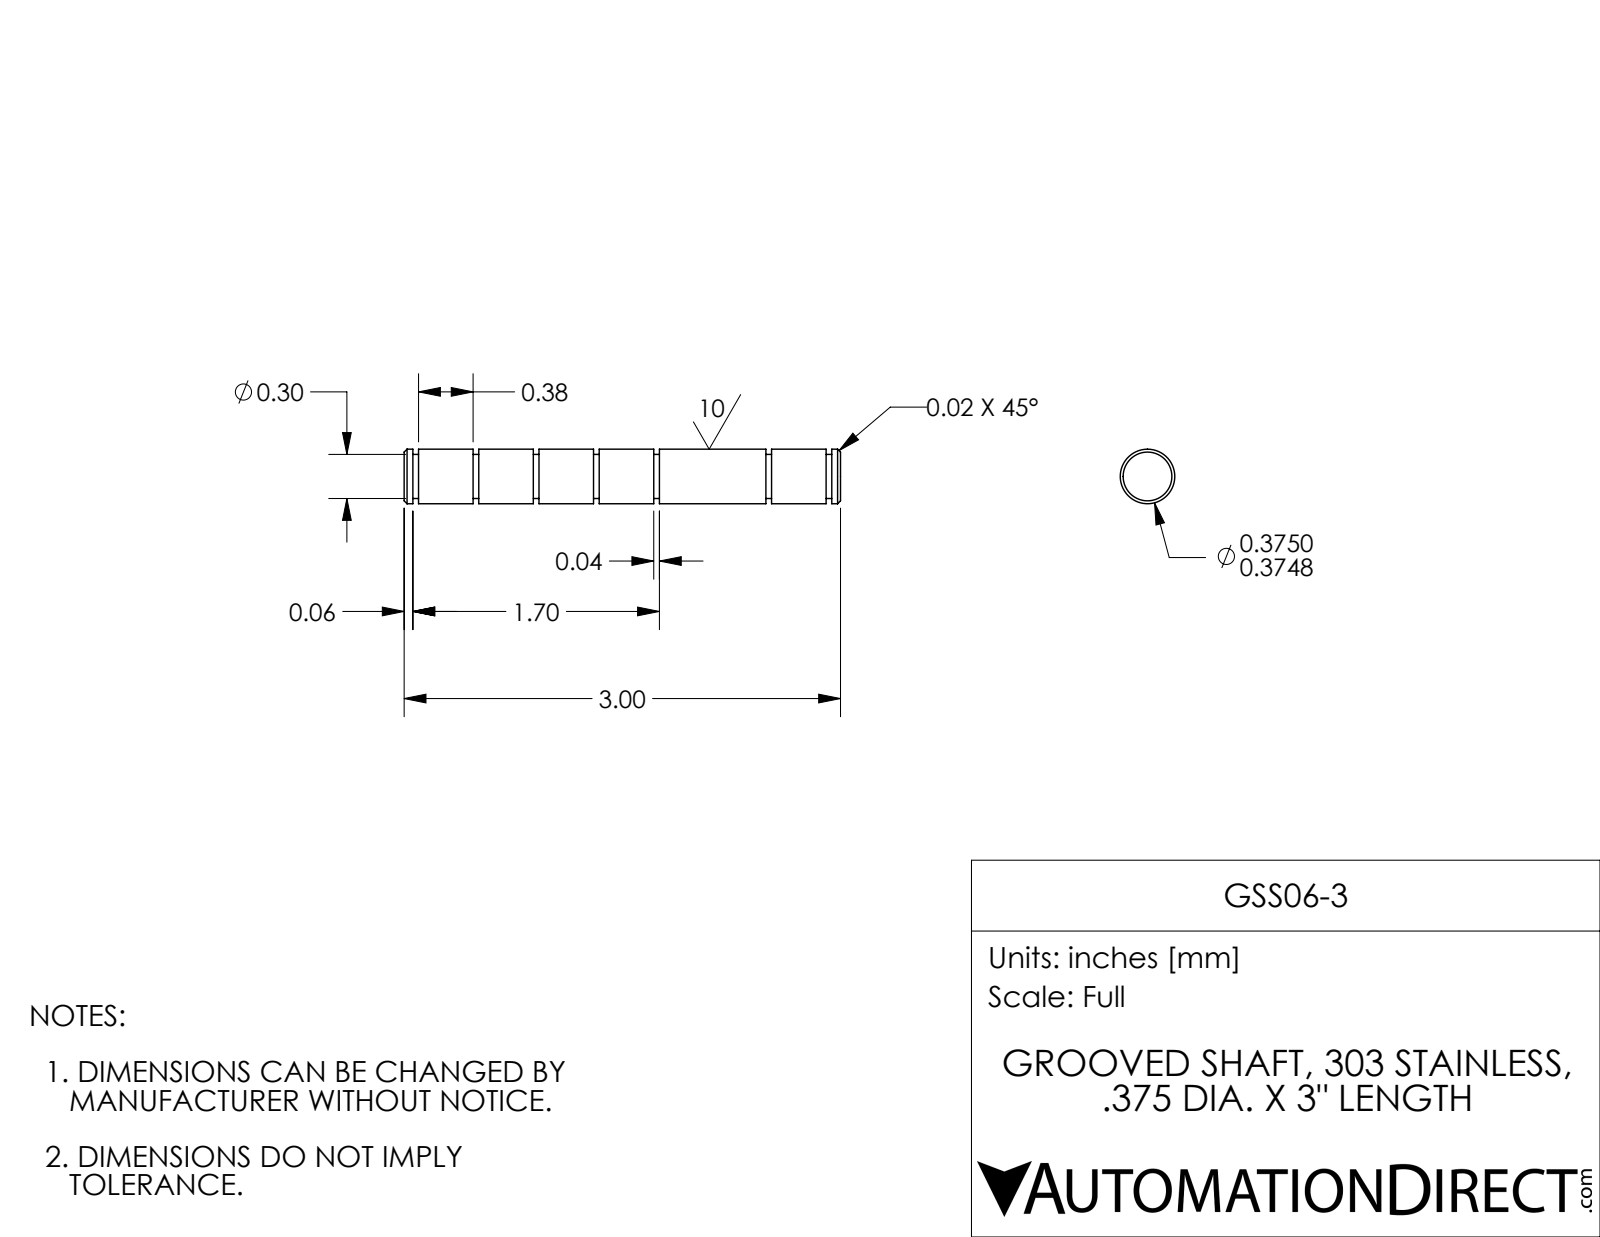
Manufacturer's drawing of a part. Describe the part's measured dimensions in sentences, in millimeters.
The part is named "GSS06-3". Its 3-D file was written by "SolidWorks 2017 (AUTOMOTIVE_DESIGN)". It is 1 solid with 50 faces: 16 planar, 30 cylindrical and 4 other. Overall it measures 76.2 by 9.5 by 9.5 millimeters. Its volume is 5 240 cubic millimeters and its surface area 2 711 square millimeters. Round bosses or shafts: 1 of diameter 9.5, 1 of diameter 7.7. The main face-to-face distances are 10.5, 1, 31.5, 61.6, 21, 51.1, 30.1, 11.5, 9.5, 76.2.
